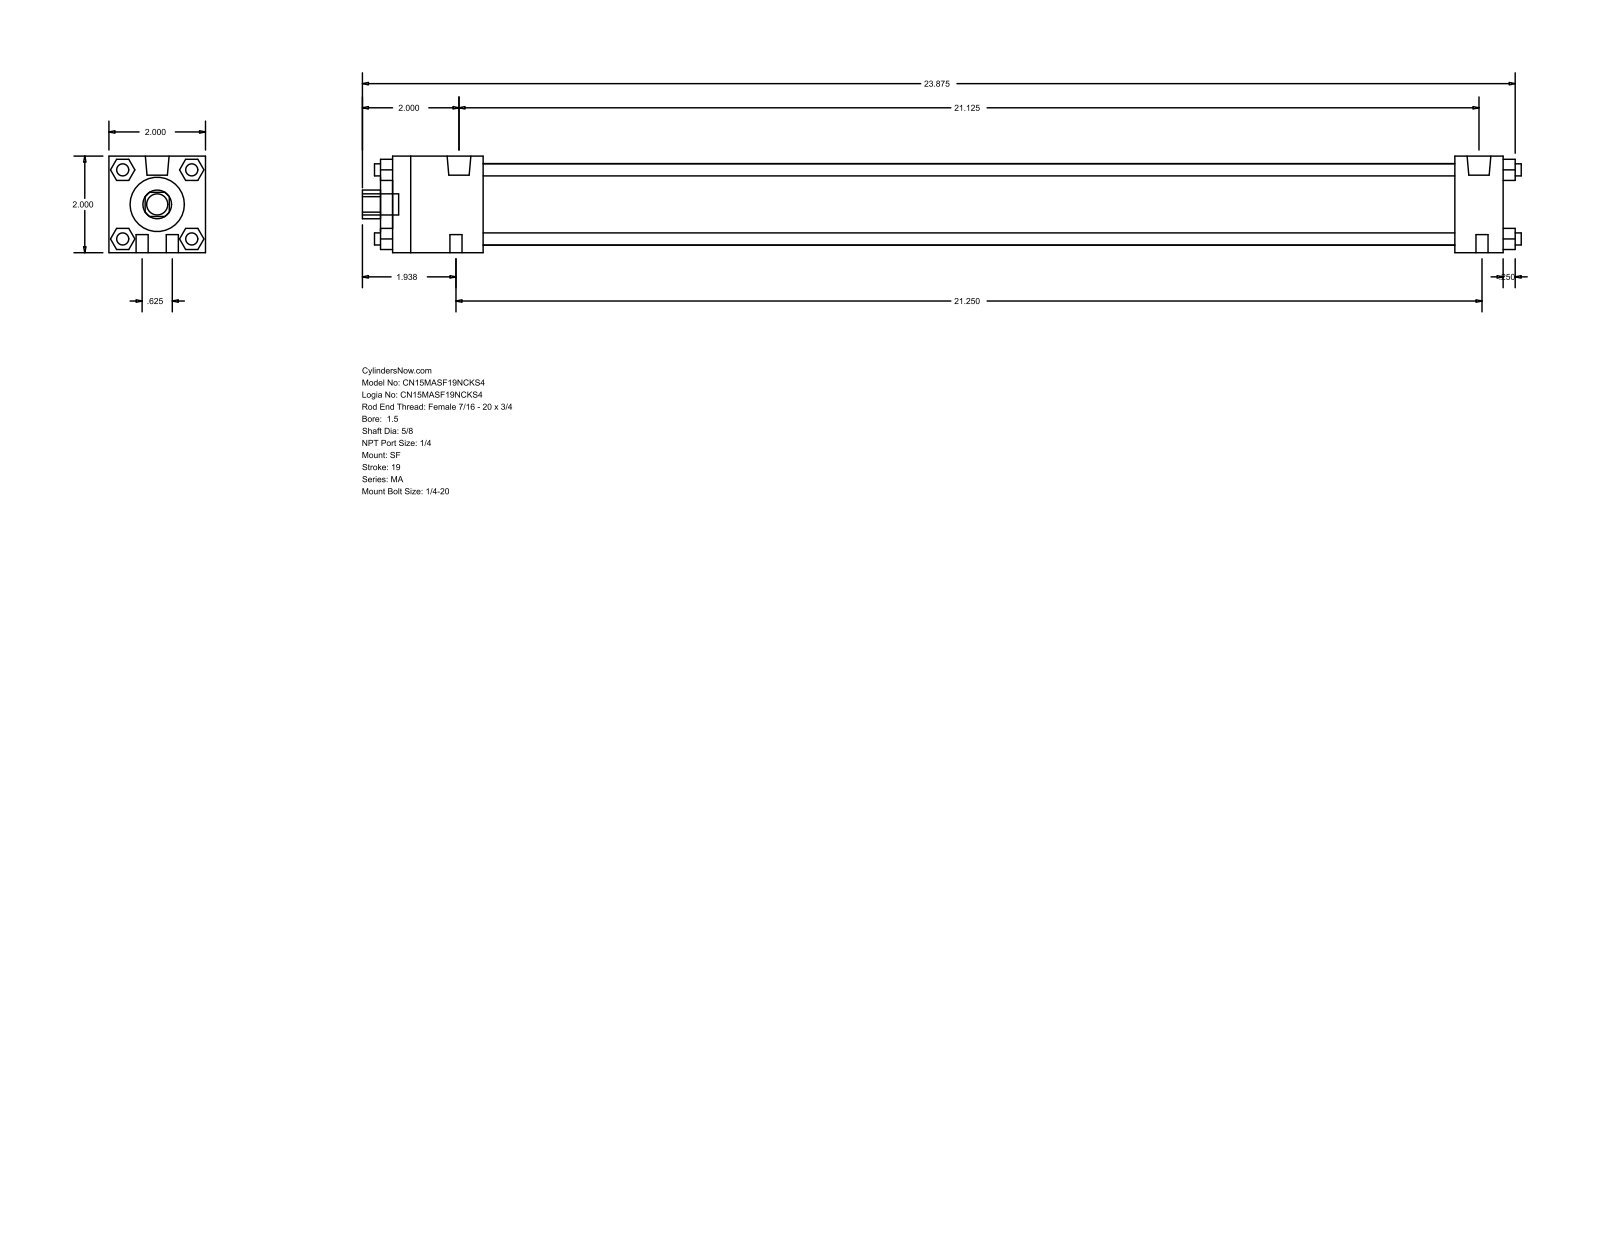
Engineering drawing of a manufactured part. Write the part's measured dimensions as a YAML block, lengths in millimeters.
part_name: "MA_SF__0150_0.625"
step_written_by: "GSSL Pune (CONFIG_CONTROL_DESIGN)"
units: millimeters
bodies: {solids: 0, faces: 124, planar: 94, cylindrical: 30, other: 0}
overall_size: [609.6, 50.8, 50.8]
round_holes:
  - {diameter: 15.88, count: 1}
  - {diameter: 28.57, count: 1}
  - {diameter: 42.93, count: 1}
round_bosses_or_shafts:
  - {diameter: 6.35, count: 8}
  - {diameter: 12.49, count: 2}
  - {diameter: 7.94, count: 2}
  - {diameter: 11.11, count: 1}
partial_cylinders:
  - {radius: 7.54, count: 1}
face_to_face_distances: [50.8, 584.2, 47.62, 558.79, 511.17, 536.58, 25.41, 6.35, 590.55, 53.97]
